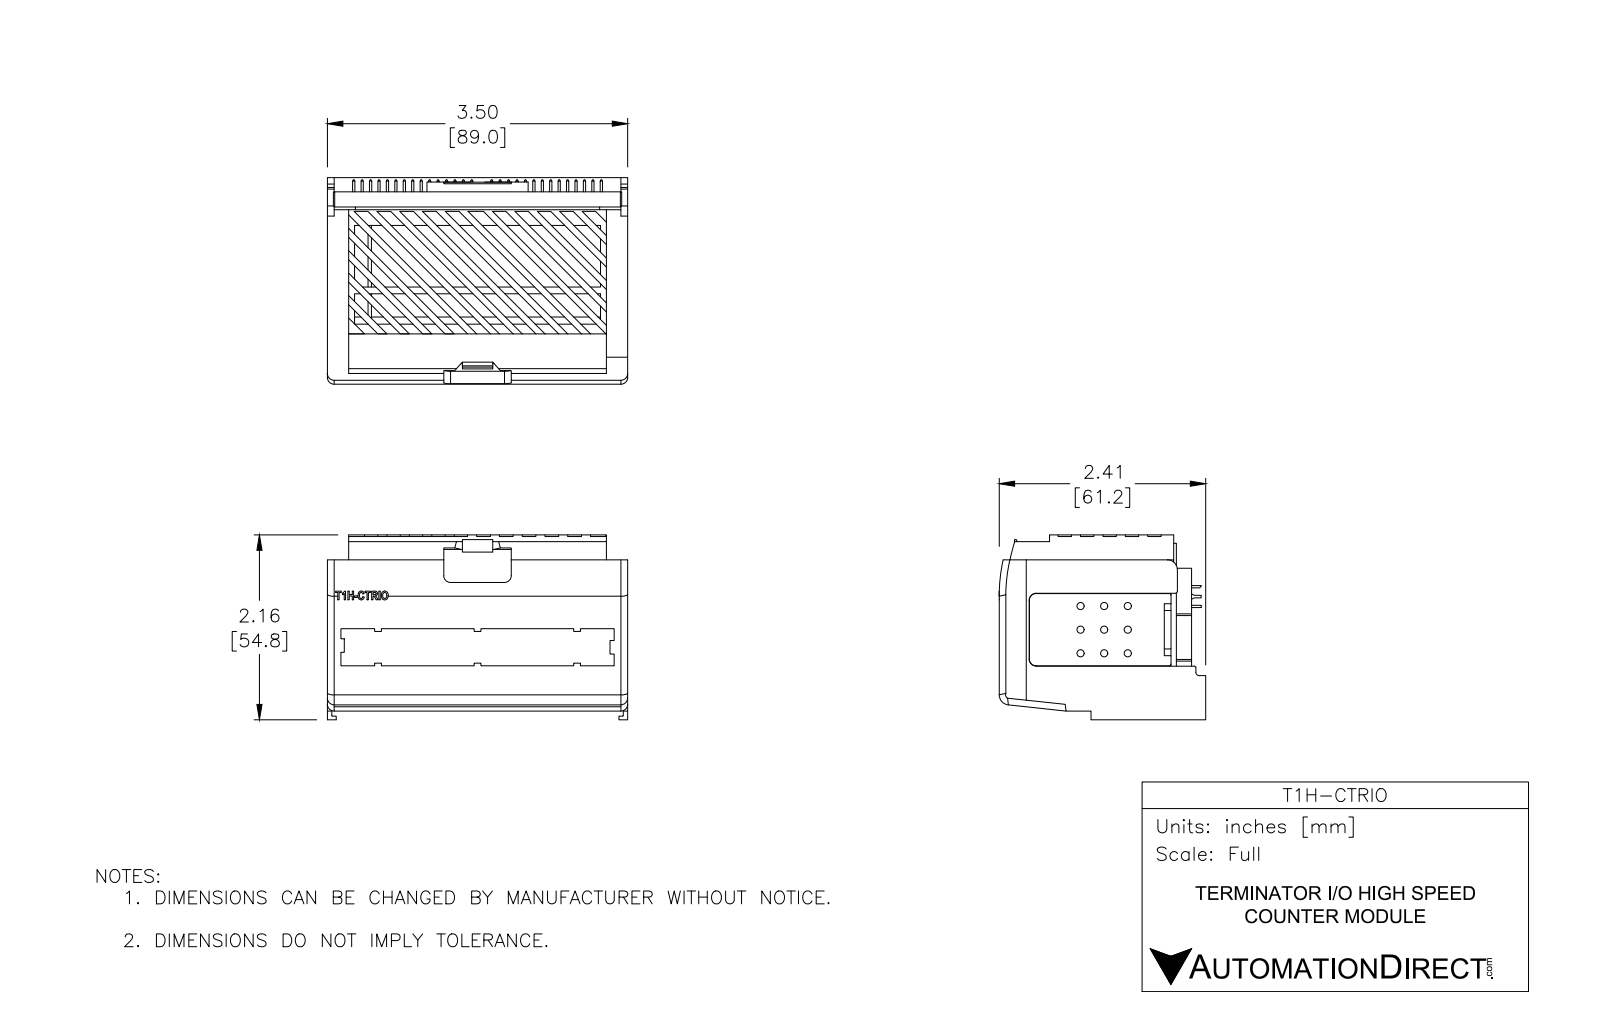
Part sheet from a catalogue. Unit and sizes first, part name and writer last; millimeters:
Units: millimetres
Overall size (bounding box): 88.7 × 65.1 × 61.36
Round holes (diameter × count): ⌀3 ×16
Round bosses / shafts (diameter × count): ⌀0.7 ×56
Partial cylindrical surfaces — rounded edges, fillets, slot ends (radius × count): R3.5 ×18, R1 ×5, R0.25 ×3, R0.55 ×3, R1.5 ×2, R8 ×1, R10 ×1, R18 ×1
Main face-to-face distances: 2, 86.7, 55.35, 0.5, 59.8, 88.7, 1.5, 55.26, 53.35, 84.7
Hole centre spacings: 5.15, 10.3, 15.45, 20.6, 25.75, 30.9, 36.05, 41.2
Volume: 45 450 mm³ · Surface area: 54 523 mm²
Bodies: 1 solid, 642 faces (438 planar, 181 cylindrical, 23 other)
Part name (STEP PRODUCT): T1H-CTRIO
STEP written by: SolidWorks 2013 (AUTOMOTIVE_DESIGN)
